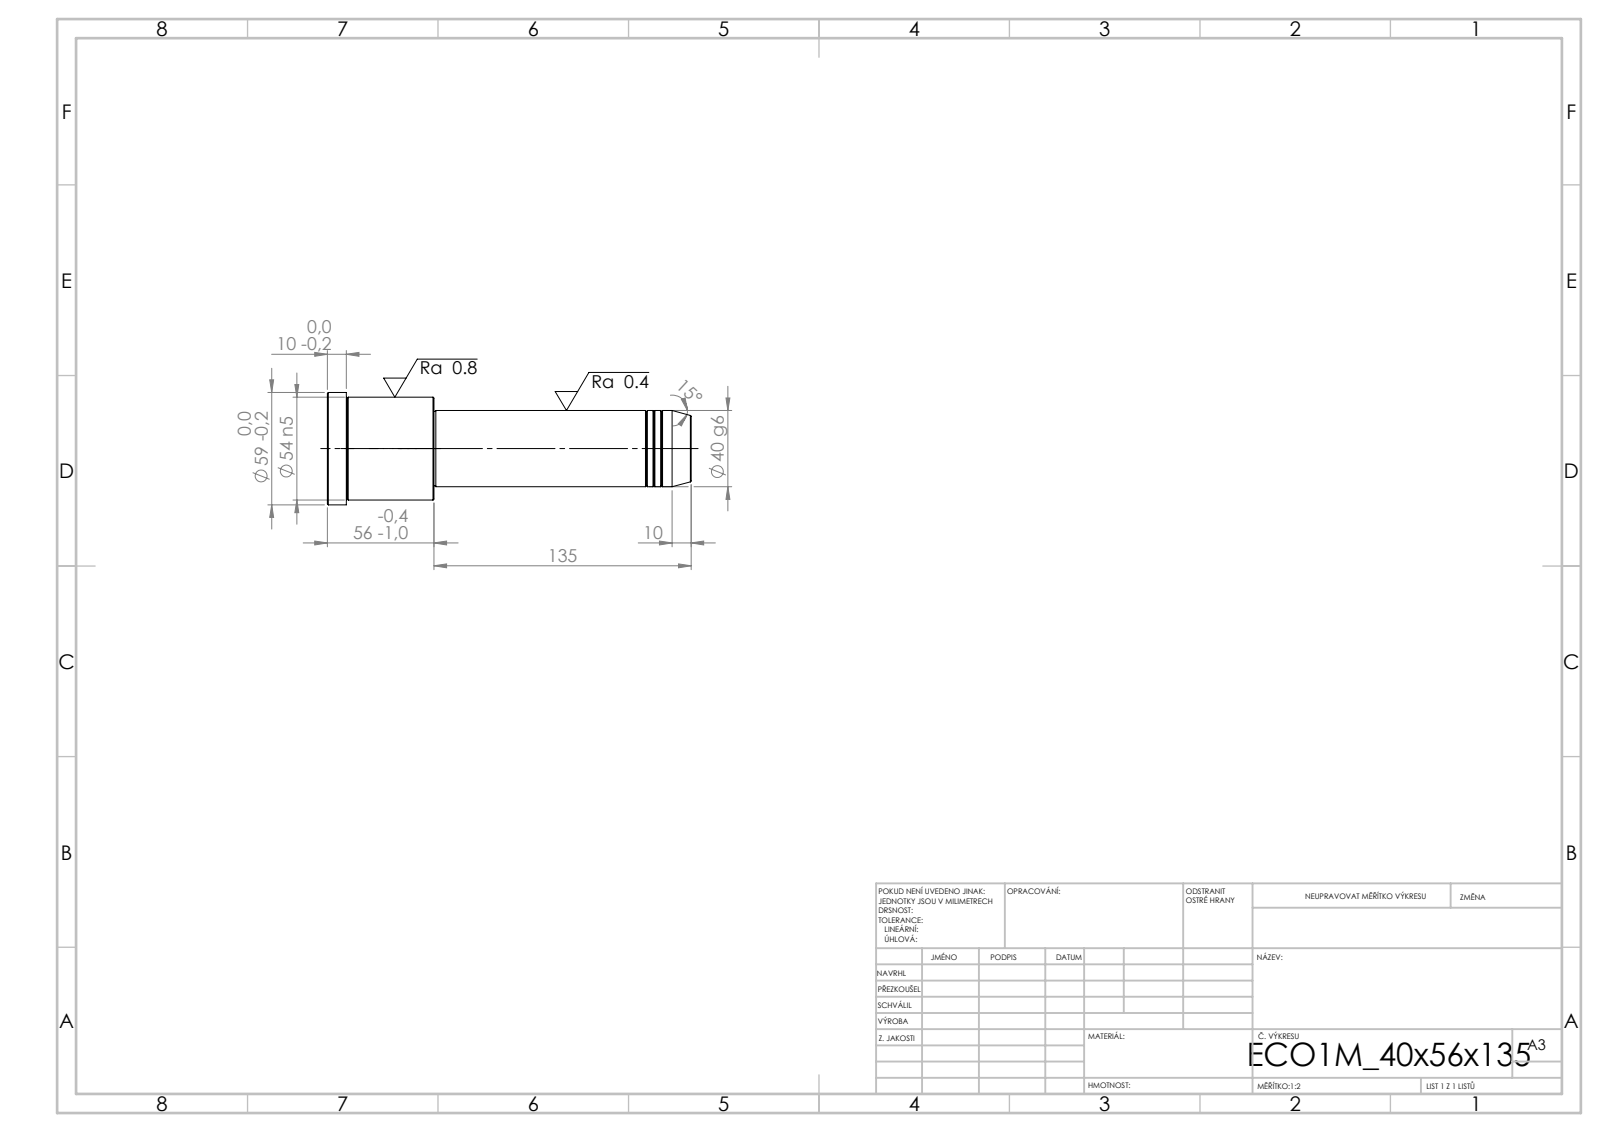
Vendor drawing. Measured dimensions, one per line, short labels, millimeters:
written by: SolidWorks 2019 (CONFIG_CONTROL_DESIGN)
unit: mm
bodies: 1 solid, 43 faces (5 planar, 14 cylindrical, 24 other)
size: 191 × 59 × 59
volume: 300 406 mm³; area: 32 036 mm²
bosses: 1× ⌀59, 1× ⌀54, 1× ⌀40, 1× ⌀39
face distances: 56, 135, 191, 181, 46, 10, 134, 1, 47, 57
